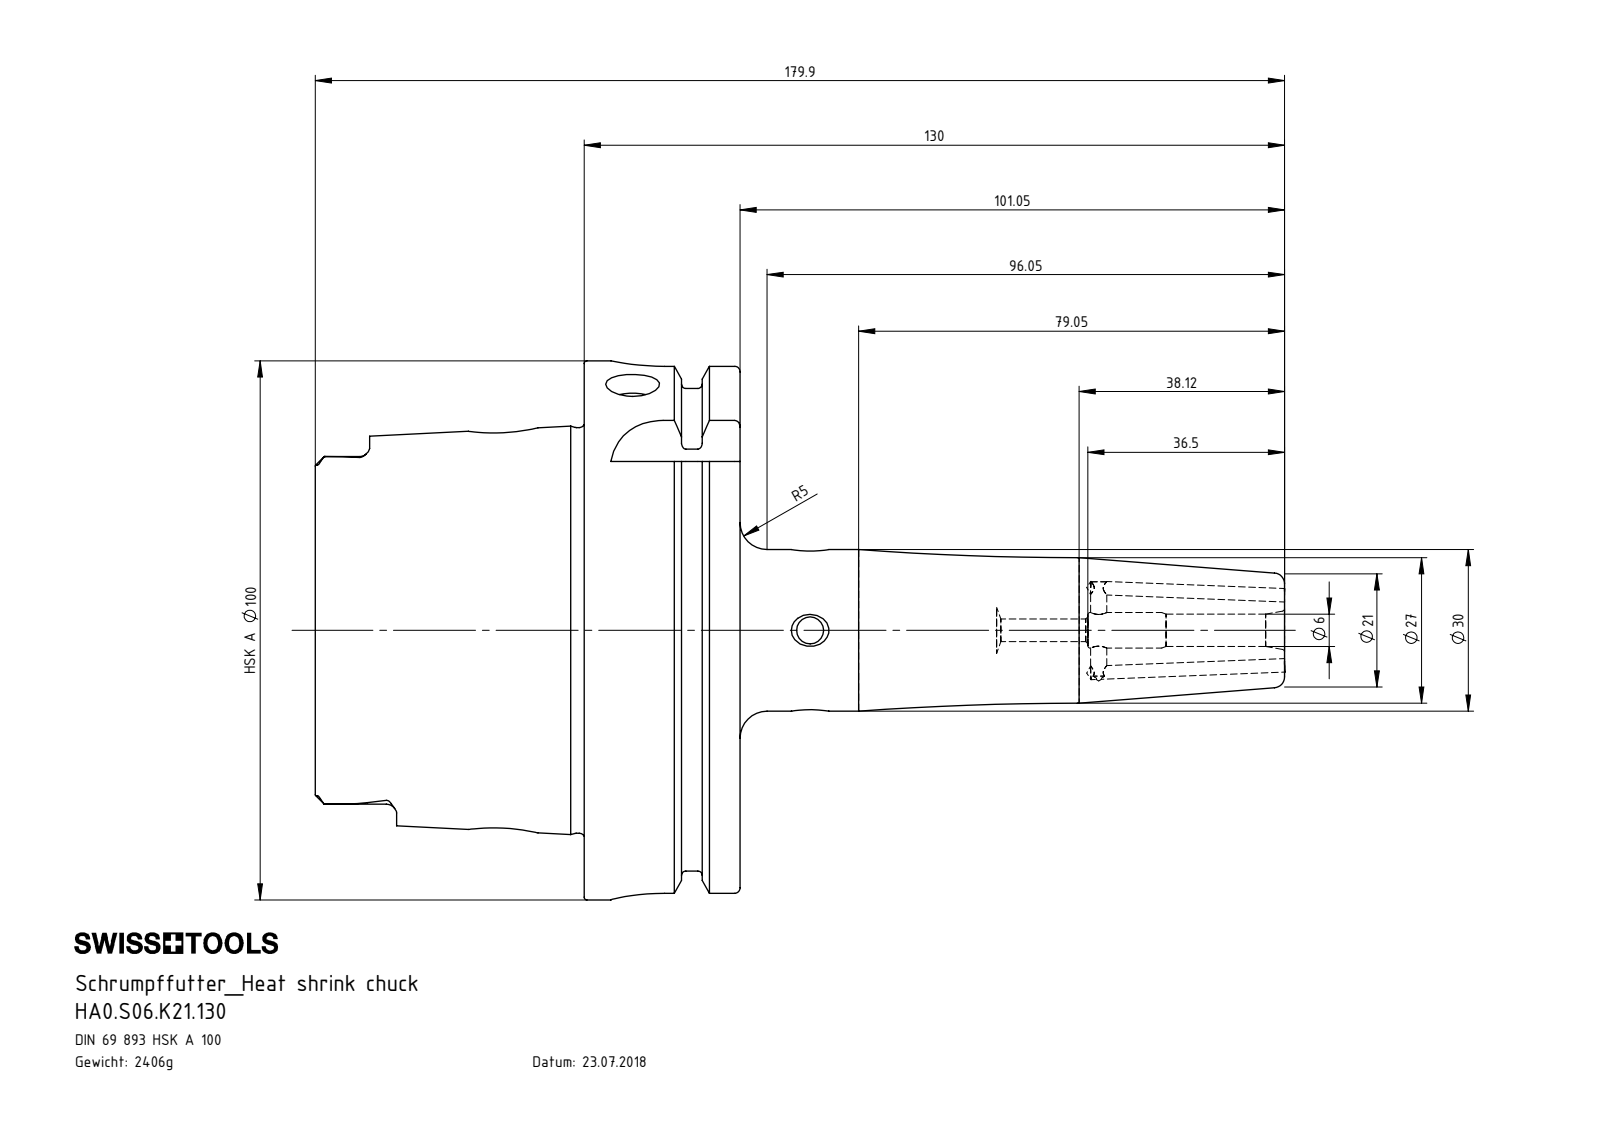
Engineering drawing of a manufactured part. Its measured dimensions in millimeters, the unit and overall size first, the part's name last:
Units: millimetres
Overall size (bounding box): 179.98 × 100 × 100
Round holes (diameter × count): ⌀2.5 ×3, ⌀10 ×3, ⌀5 ×2, ⌀3 ×1, ⌀4.2 ×1, ⌀6 ×1, ⌀6.6 ×1, ⌀8.5 ×1, ⌀12 ×1, ⌀22.5 ×1, ⌀26 ×1, ⌀53 ×1
Round bosses / shafts (diameter × count): ⌀3 ×2, ⌀100 ×1, ⌀91.95 ×1, ⌀75.26 ×1, ⌀30 ×1, ⌀27 ×1, ⌀5 ×1
Partial cylindrical surfaces — rounded edges, fillets, slot ends (radius × count): R1.9 ×6, R4.88 ×4, R10 ×4
Main face-to-face distances: 28.95, 12.45, 16.5, 49.9, 62.35, 78.85, 78.2, 28.3, 15.85, 0.65
Hole centre spacings: 34.95, 53.55, 56.95, 110.5
Volume: 306 449 mm³ · Surface area: 61 676 mm²
Bodies: 4 solids, 306 faces (95 planar, 91 cylindrical, 120 other)
Part name (STEP PRODUCT): HA0.S06.K21.130; ERU-CJ2.001.006; HA0-S06.K21.130_C_Fertigbearbeitung; ERU-AN1.K01.014_A
STEP written by: SolidWorks 2017 (AUTOMOTIVE_DESIGN)
